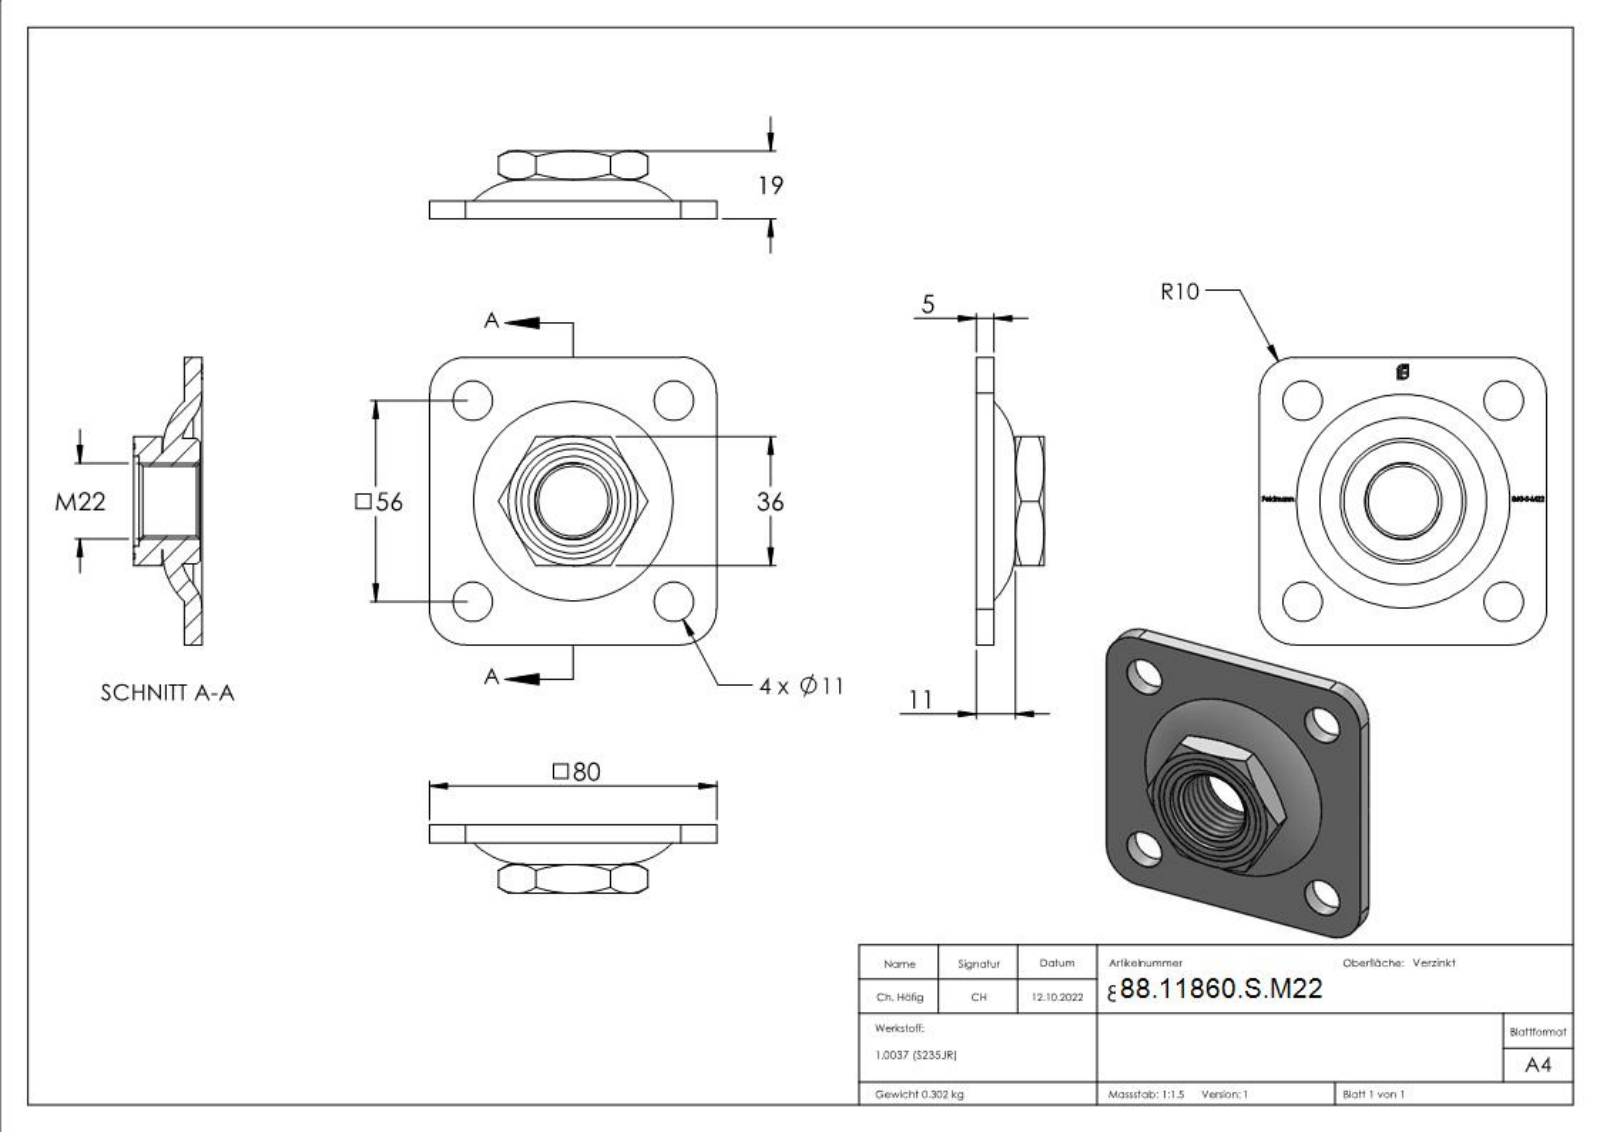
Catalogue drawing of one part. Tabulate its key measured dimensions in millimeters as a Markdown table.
| quantity | value |
| --- | --- |
| part name | 860-S-M22 |
| STEP written by | SolidWorks 2018 (CONFIG_CONTROL_DESIGN) |
| units | millimeters |
| bodies | 1 solid, 318 faces (157 planar, 13 cylindrical, 148 other) |
| overall size | 80 × 80 × 19 |
| volume | 38 767 mm³ |
| surface area | 17 561 mm² |
| round holes (diameter × count) | 11 × 4, 19.5 × 1, 25 × 1, 32 × 1 |
| round bosses / shafts (diameter × count) | 35 × 1, 29 × 1 |
| partial cylindrical surfaces (radius × count) | 10 × 4 |
| main face-to-face distances | 5, 80, 0.5, 4.5, 6, 11, 10.5, 36, 19, 18.5 |
| hole center spacings | 39.6, 56, 79.2 |
